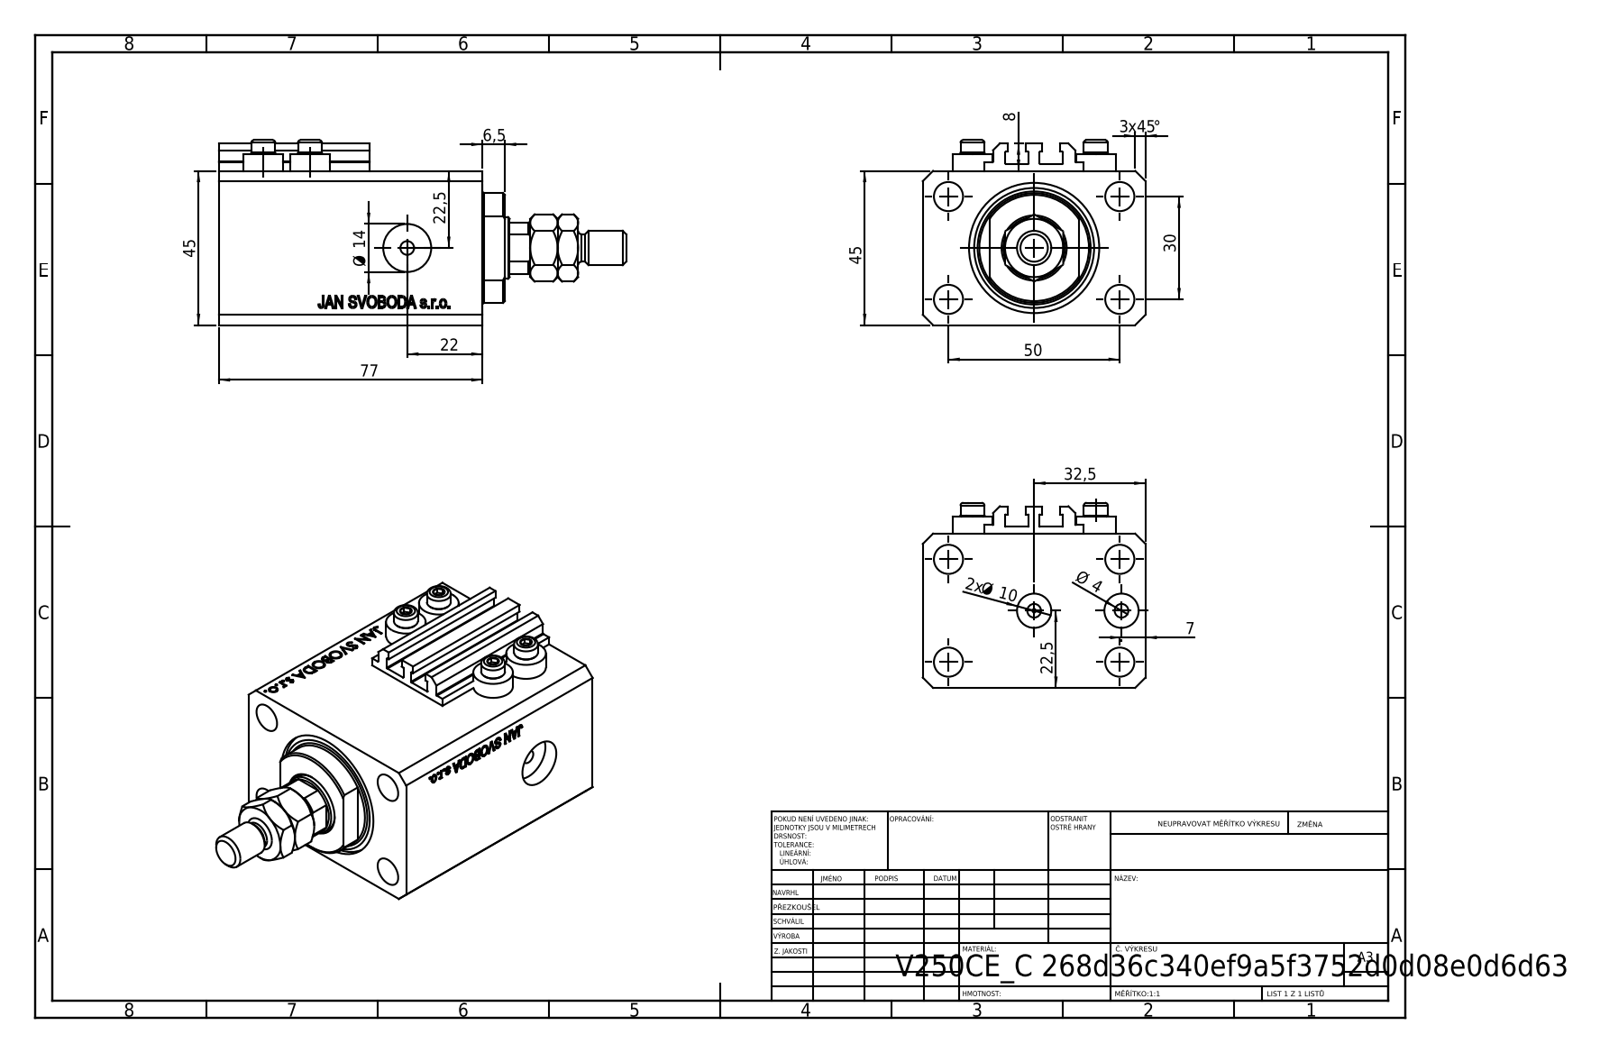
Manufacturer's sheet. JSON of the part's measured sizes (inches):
{"part_name": "V250CE_C_VCP; ALLEN BOLT V250CE; V250CE_VC_C; MTA (+1 more)", "step_written_by": "SolidWorks 2019 (CONFIG_CONTROL_DESIGN)", "units": "inches", "bodies": {"solids": 9, "faces": 1091, "planar": 519, "cylindrical": 96, "other": 476}, "overall_size": [4.681, 2.559, 2.126], "volume_in3": 13.18, "surface_area_in2": 95.31, "round_holes": [[0.157, 8], [0.335, 5], [0.394, 2], [0.551, 2], [0.049, 1], [0.709, 1], [0.984, 1], [1.496, 1]], "round_bosses_or_shafts": [[0.457, 4], [0.276, 4], [0.315, 1]], "partial_cylinders_radius": [[0.008, 10], [0.335, 1], [0.63, 1]], "face_to_face_distances": [1.772, 2.559, 3.031, 2.043, 0.988, 0.272, 2.76, 0.118, 1.85, 0.236], "hole_center_spacings": [1.148, 0.535, 0.591, 1.181, 1.417, 1.515, 1.969, 2.074]}
